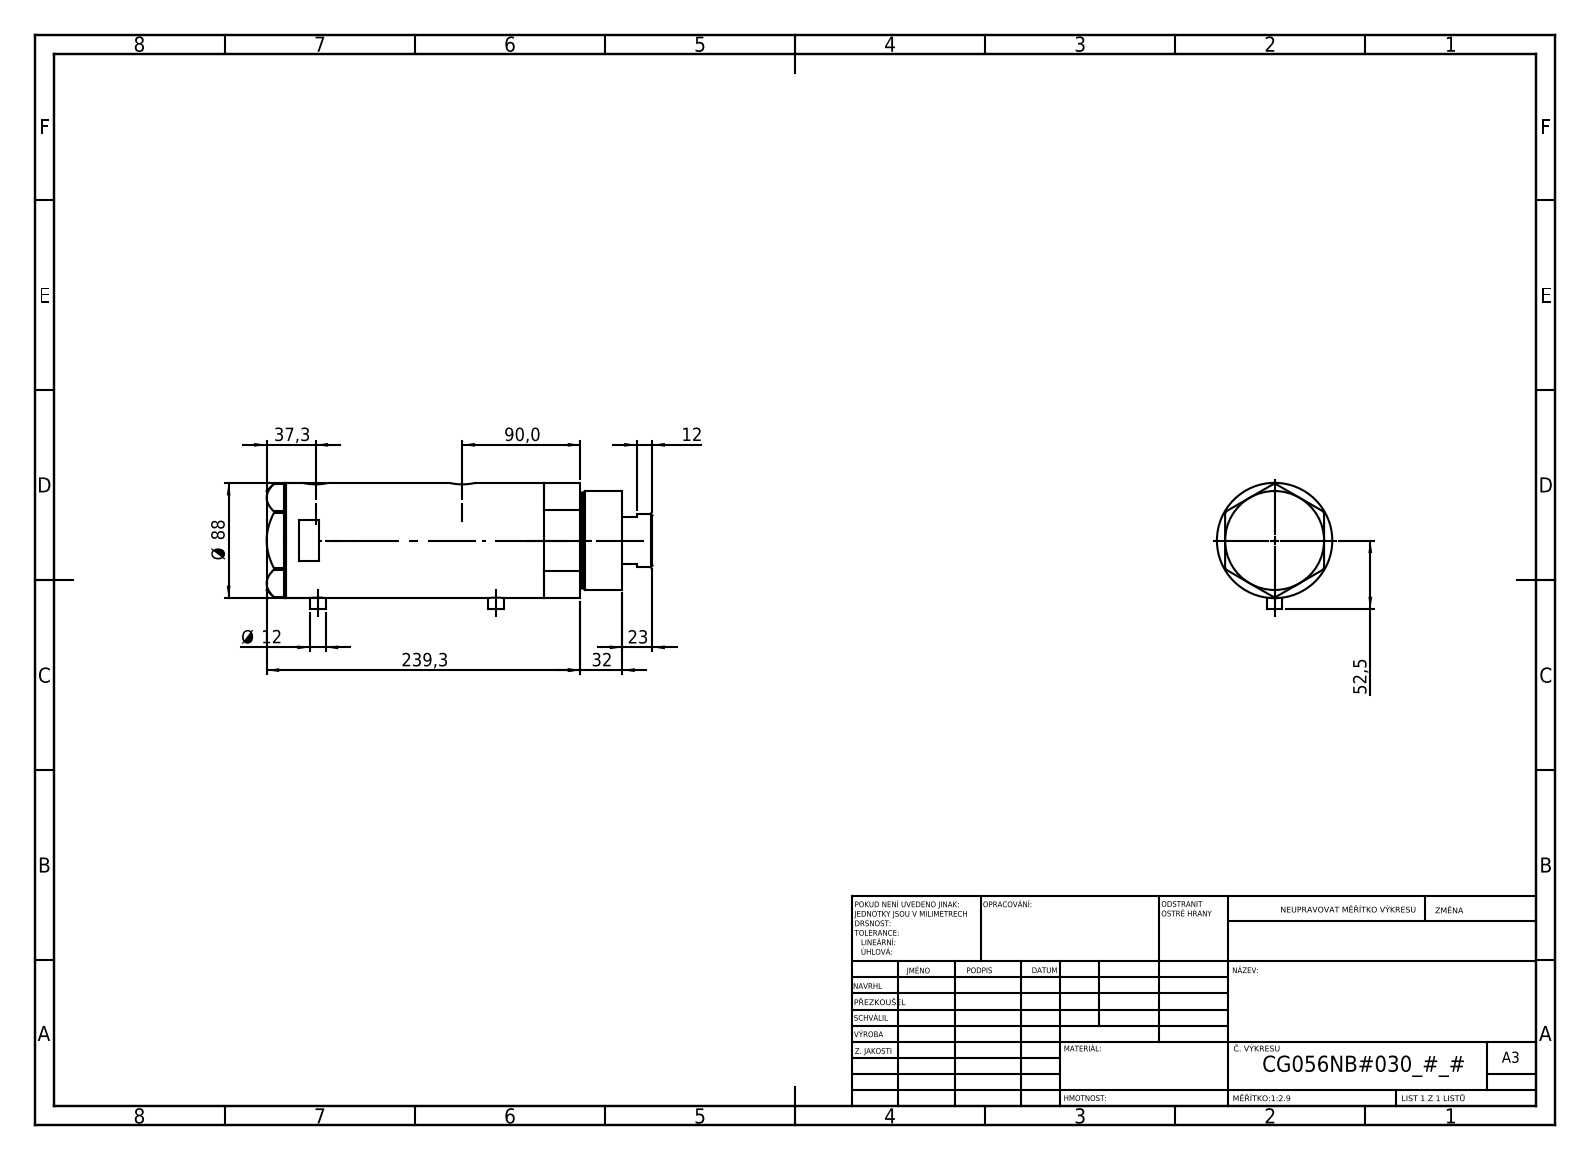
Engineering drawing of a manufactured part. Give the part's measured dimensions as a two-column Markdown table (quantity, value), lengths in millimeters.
| quantity | value |
| --- | --- |
| part name | V270CG_BACK; V270CG_FRONT; V270CG_VC; V270CG_MIDDLE |
| STEP written by | SolidWorks 2019 (CONFIG_CONTROL_DESIGN) |
| units | millimeters |
| bodies | 4 solids, 121 faces (52 planar, 49 cylindrical, 20 other) |
| overall size | 294.3 × 96.5 × 88 |
| volume | 1 556 000 mm³ |
| surface area | 222 314 mm² |
| round holes (diameter × count) | 12.5 × 2, 13.16 × 2, 20 × 2, 14.5 × 1, 42 × 1, 43.5 × 1, 56 × 1, 60 × 1, 80 × 1 |
| round bosses / shafts (diameter × count) | 12 × 2, 88 × 1, 75 × 1, 73 × 1, 41 × 1 |
| main face-to-face distances | 134.4, 26, 108.4, 15, 41, 149.4, 256.3, 271.3, 230.3, 121.9 |
| hole center spacings | 1.7, 25.8, 110.3, 112, 136.1, 137.8 |
